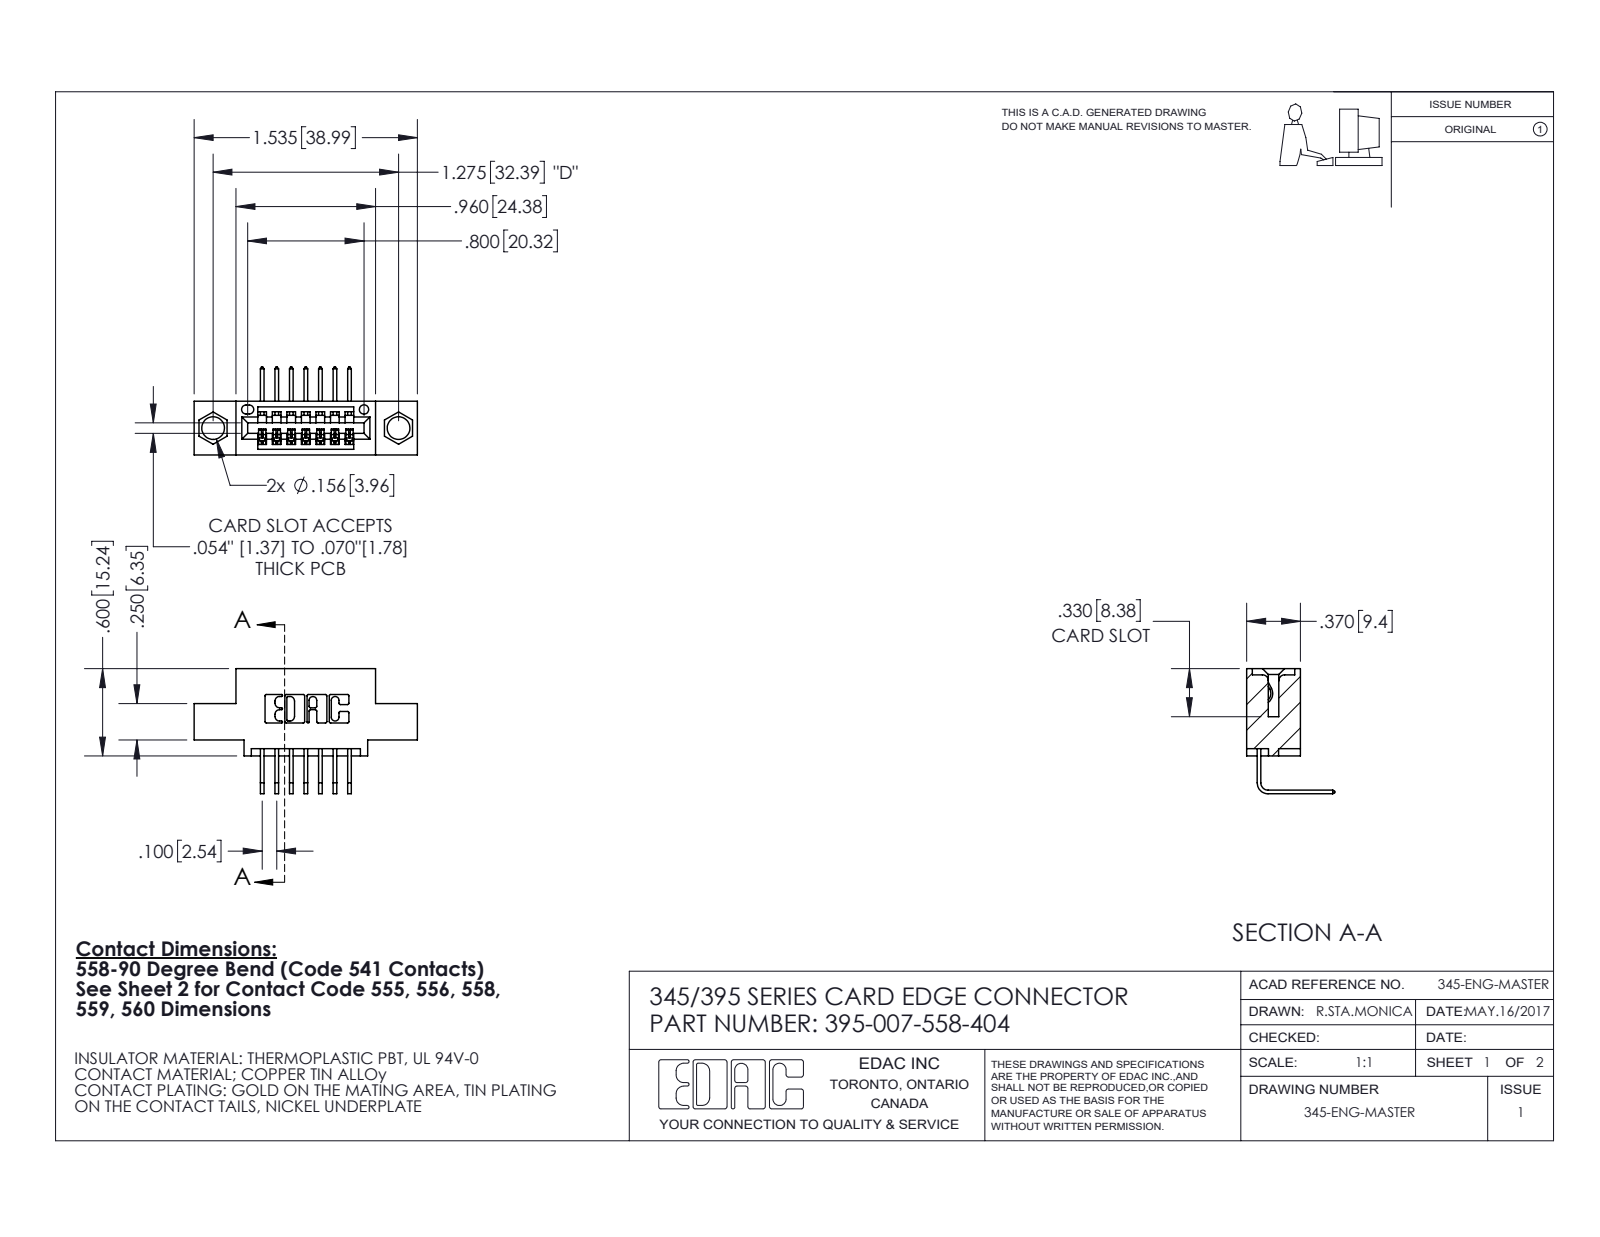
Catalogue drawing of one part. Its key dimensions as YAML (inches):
part_name: "345 Part_0.110 Offset - 0.156 Dia-TI; 395-007-558-404; 345-292-001_558 Tail - 2"
step_written_by: "SolidWorks 2020 (CONFIG_CONTROL_DESIGN)"
units: inches
bodies: {solids: 8, faces: 564, planar: 392, cylindrical: 172, other: 0}
overall_size: [1.535, 0.859, 0.605]
volume: 0.199
surface_area: 6.074
round_holes:
  - {diameter: 0.156, count: 2}
  - {diameter: 0.064, count: 1}
partial_cylinders:
  - {radius: 0.01, count: 22}
  - {radius: 0.006, count: 14}
  - {radius: 0.007, count: 6}
  - {radius: 0.031, count: 6}
  - {radius: 0.026, count: 3}
  - {radius: 0.031, count: 2}
  - {radius: 0.04, count: 2}
  - {radius: 0.014, count: 1}
face_to_face_distances: [0.2, 0.37, 0.072, 0.298, 0.1, 0.3, 0.098, 0.272, 0.025, 0.16]
hole_center_spacings: [0.27, 1.045, 1.275]
